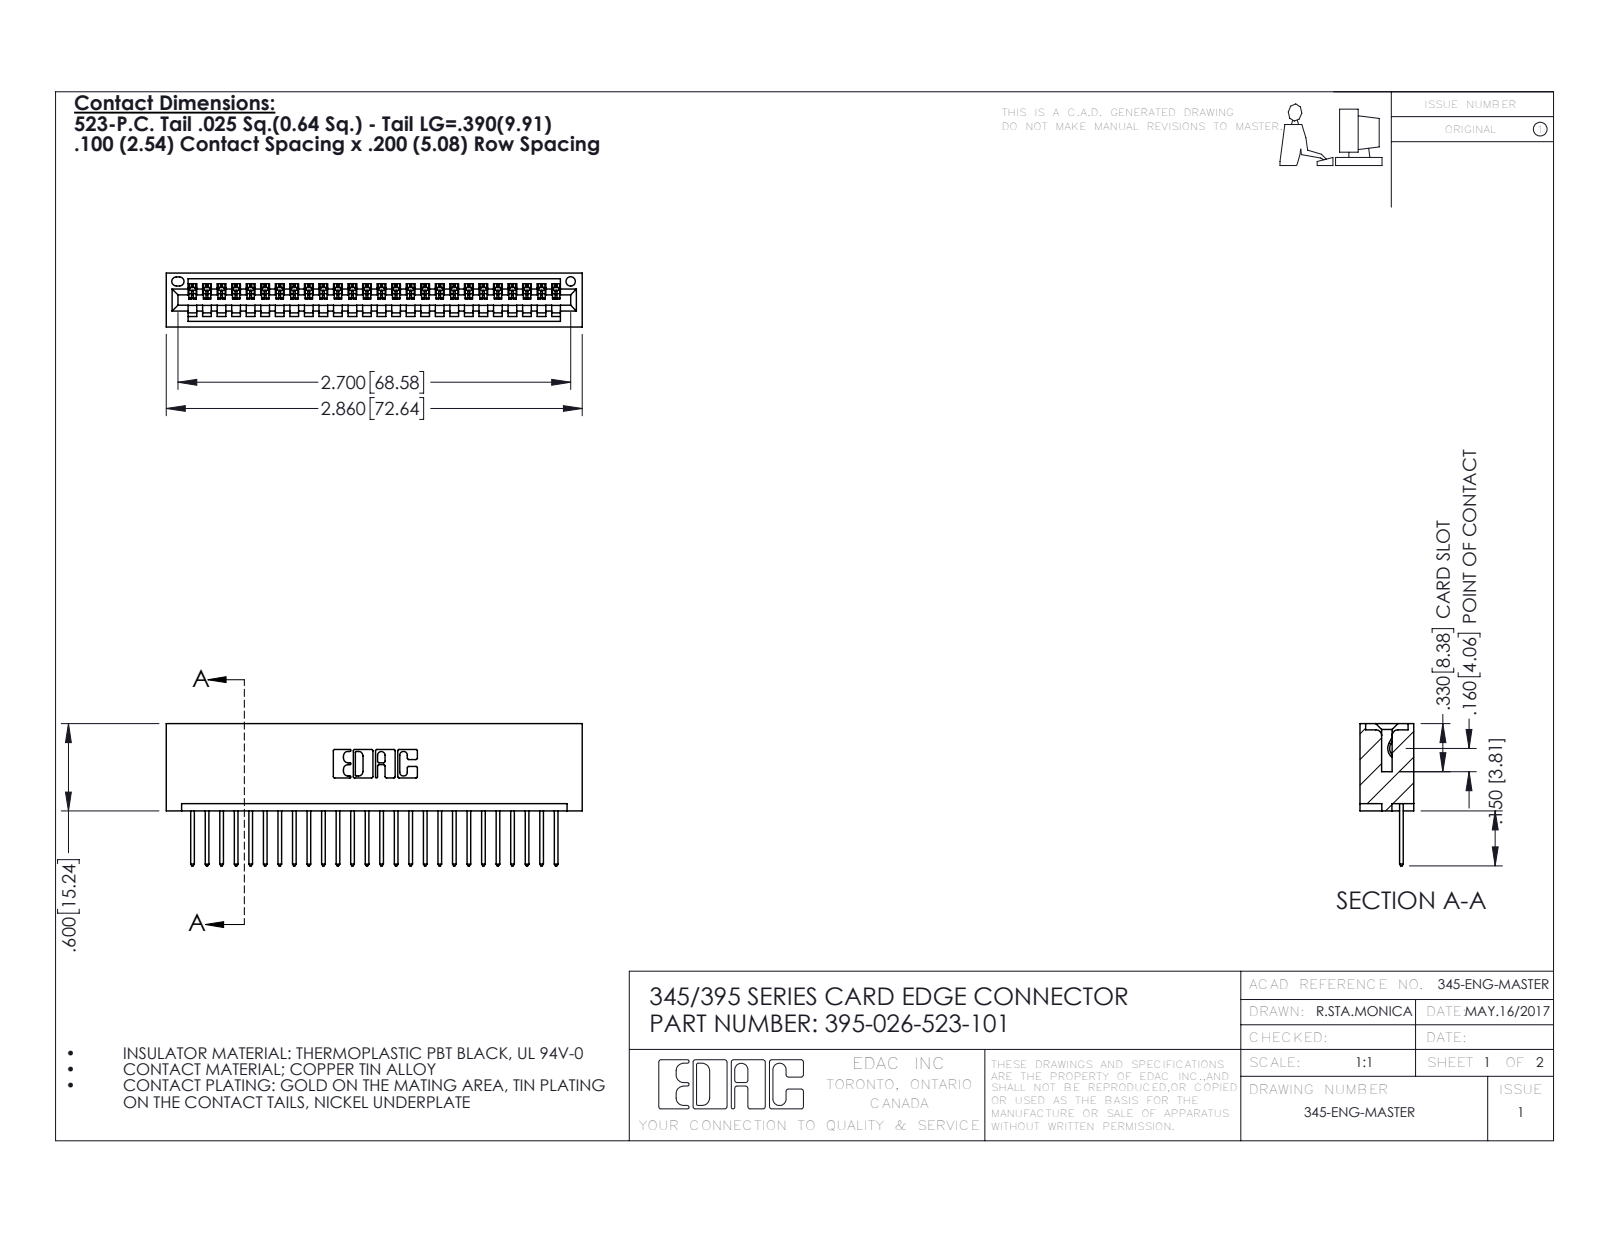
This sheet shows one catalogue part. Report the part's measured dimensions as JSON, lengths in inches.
{"part_name": "345-292-001_345-293-123; 395-026-523-101; 345 Part_No Mounting Lugs", "step_written_by": "SolidWorks 2016 (CONFIG_CONTROL_DESIGN)", "units": "inches", "bodies": {"solids": 27, "faces": 1626, "planar": 1116, "cylindrical": 510, "other": 0}, "overall_size": [2.86, 0.977, 0.37], "volume_in3": 0.448, "surface_area_in2": 15.13, "round_holes": [[0.064, 1]], "partial_cylinders_radius": [[0.006, 52], [0.01, 52], [0.01, 22], [0.007, 6], [0.031, 6], [0.026, 3], [0.031, 2], [0.04, 2]], "face_to_face_distances": [0.298, 0.072, 0.2, 0.37, 0.098, 0.272, 0.025, 0.225, 0.149, 0.072]}
